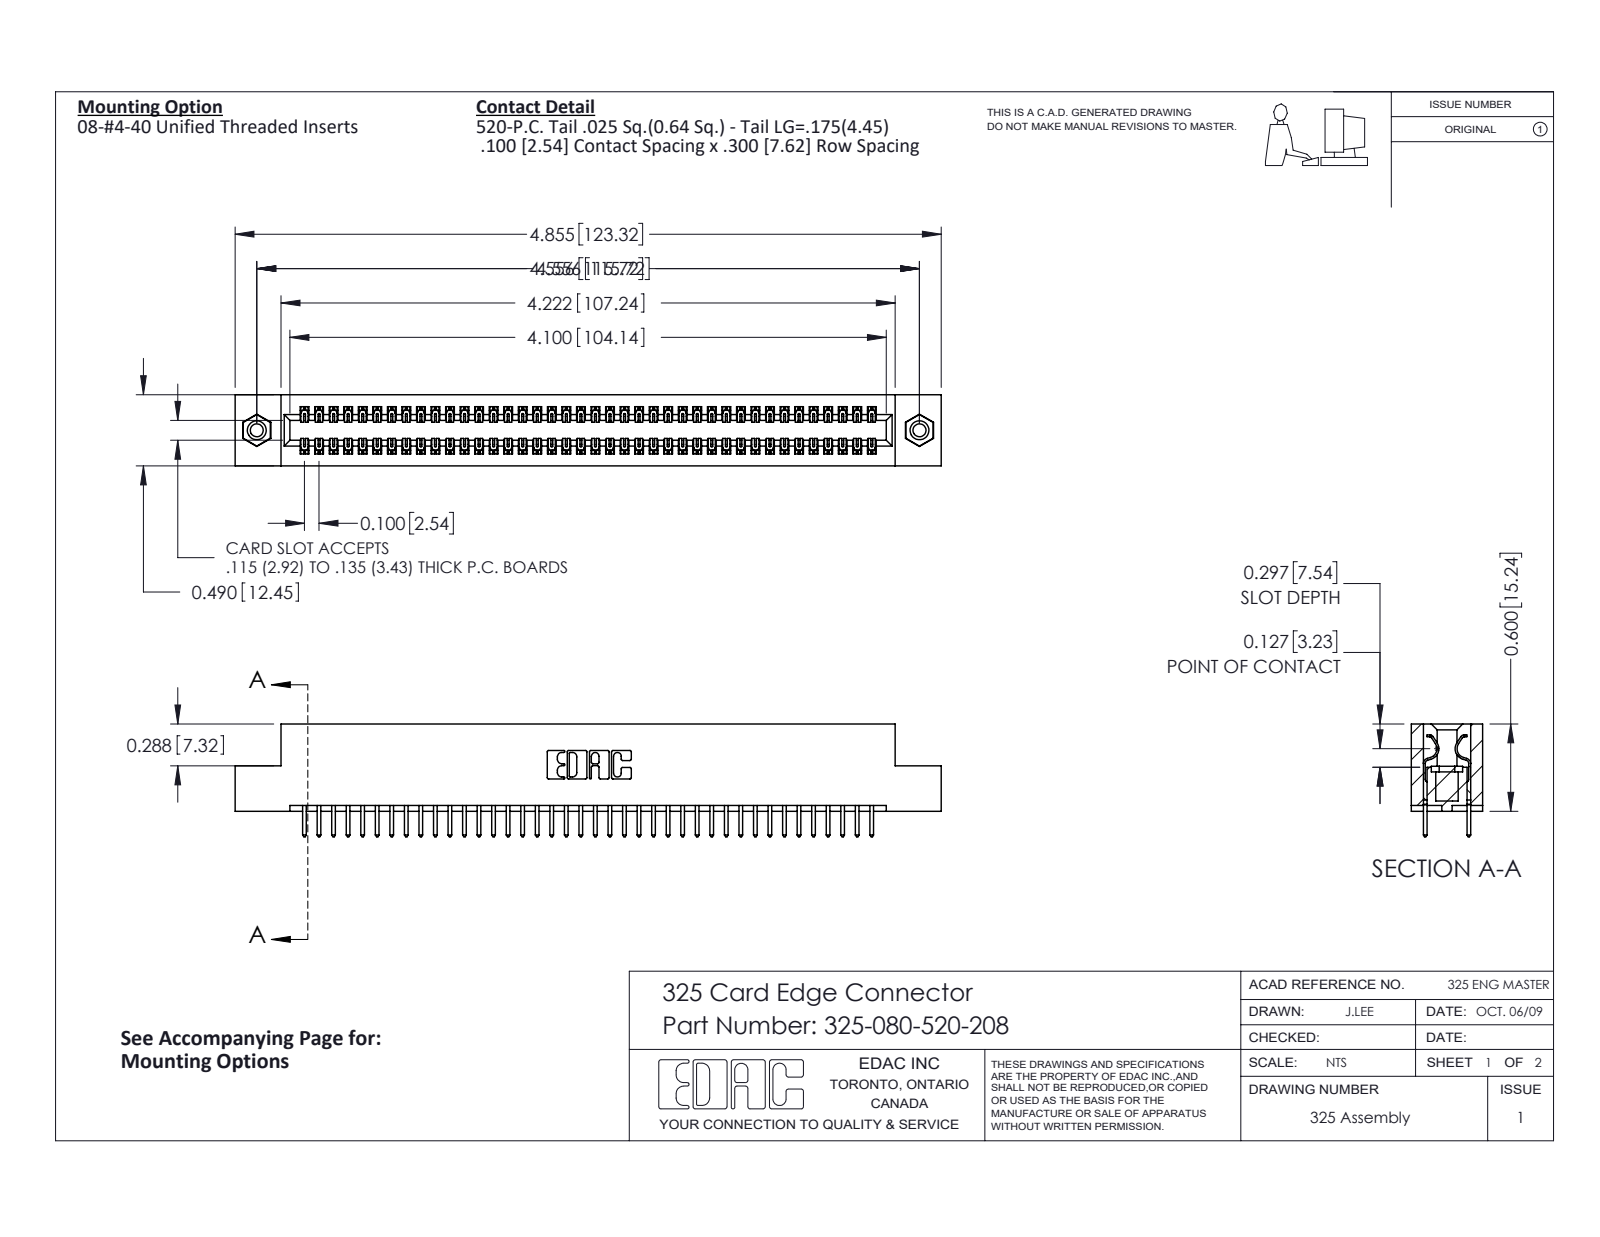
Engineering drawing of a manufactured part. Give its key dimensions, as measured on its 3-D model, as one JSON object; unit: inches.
{"part_name": "325 Part_TI; 325-080-520-208; 345-250-001_345-250-003-102; 325-292-001_325-293-120", "step_written_by": "SolidWorks 2016 (CONFIG_CONTROL_DESIGN)", "units": "inches", "bodies": {"solids": 83, "faces": 4334, "planar": 2982, "cylindrical": 1336, "other": 16}, "overall_size": [4.855, 0.775, 0.49], "volume_in3": 0.969, "surface_area_in2": 29.5, "round_holes": [[0.089, 2], [0.125, 2], [0.16, 2]], "round_bosses_or_shafts": [[0.155, 2]], "partial_cylinders_radius": [[0.006, 120], [0.01, 80], [0.01, 22], [0.007, 6], [0.031, 6], [0.026, 3], [0.014, 2], [0.022, 2]], "face_to_face_distances": [0.083, 0.407, 0.49, 0.3, 0.107, 0.383, 0.025, 0.325, 0.275, 0.56], "hole_center_spacings": [4.556]}
